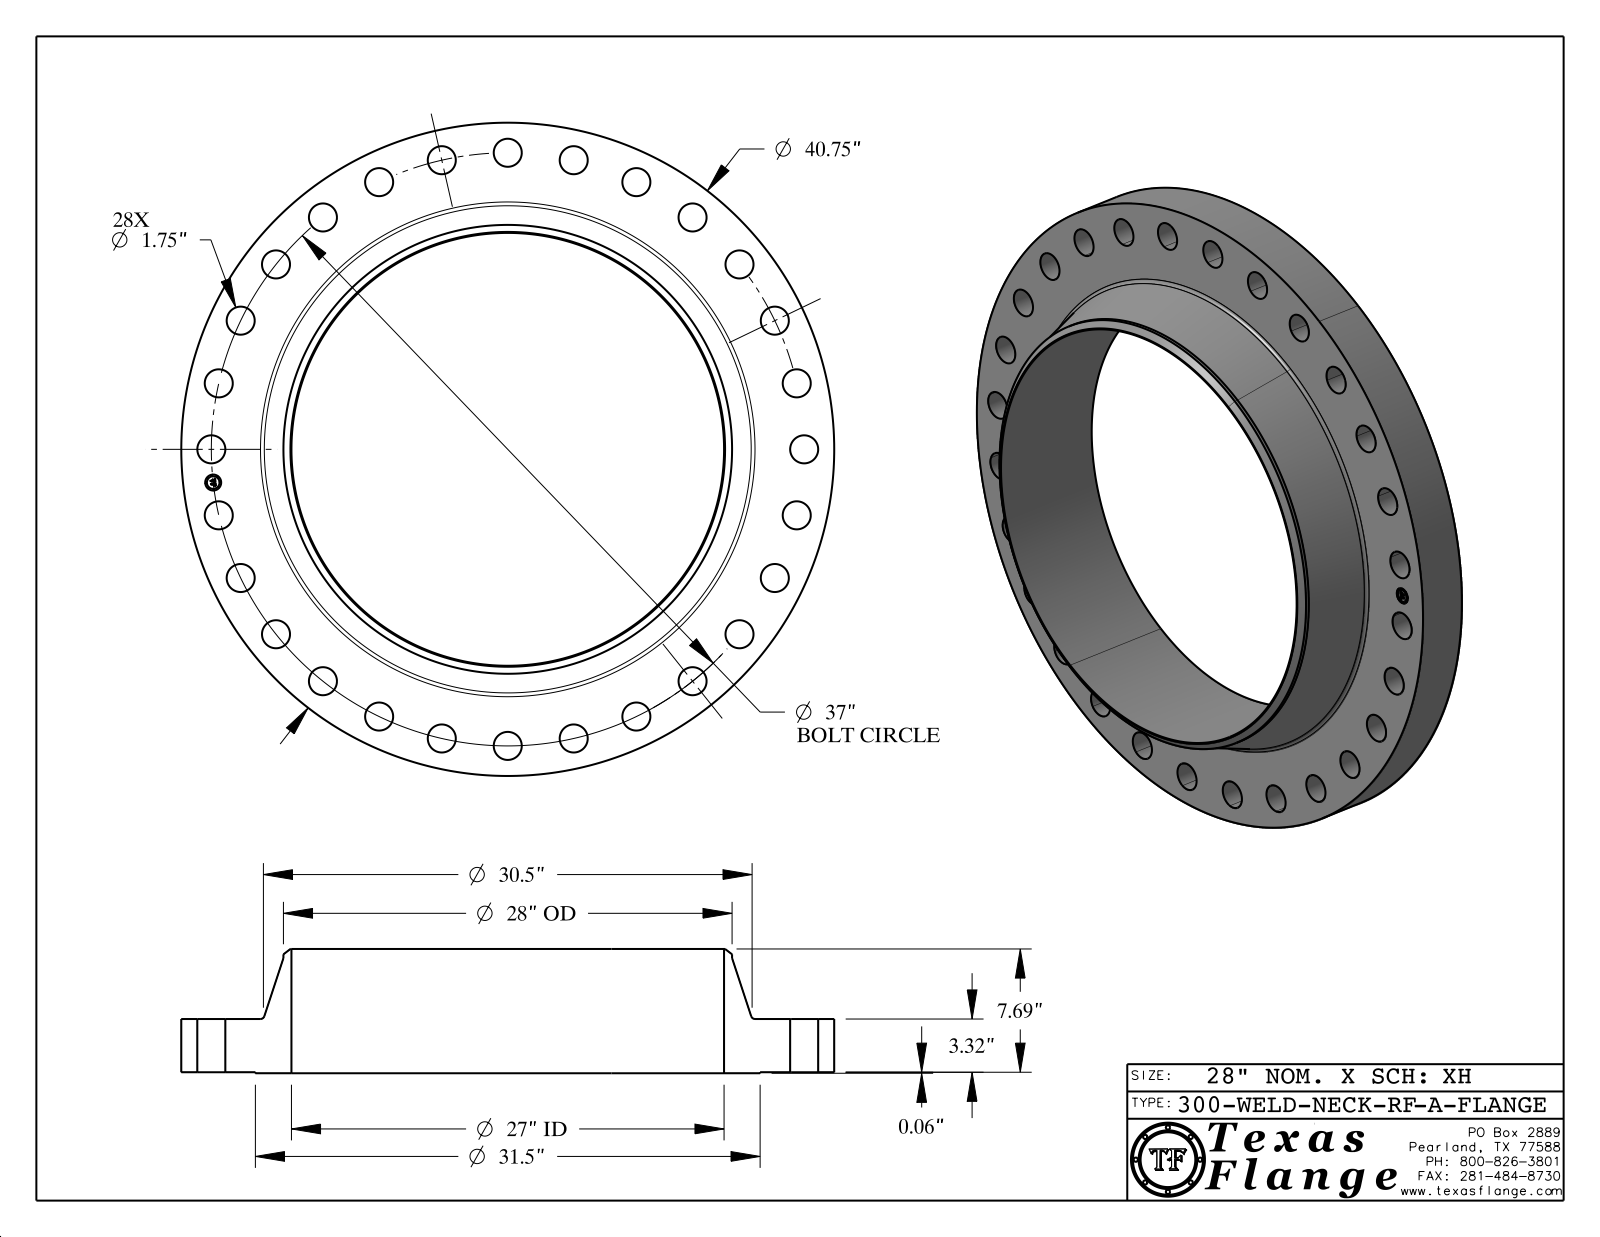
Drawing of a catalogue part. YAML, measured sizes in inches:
part_name: "300-WELD-NECK-RF, Series A"
step_written_by: "CATIA V5 STEP AP214 (AUTOMOTIVE_DESIGN)"
units: inches
bodies: {solids: 1, faces: 459, planar: 369, cylindrical: 84, other: 6}
overall_size: [40.75, 40.75, 7.753]
volume: 2616
surface_area: 3207
round_holes:
  - {diameter: 1.75, count: 28}
  - {diameter: 1, count: 1}
  - {diameter: 27, count: 1}
round_bosses_or_shafts:
  - {diameter: 0.061, count: 8}
  - {diameter: 40.75, count: 1}
  - {diameter: 31.5, count: 1}
  - {diameter: 28, count: 1}
  - {diameter: 0.788, count: 1}
face_to_face_distances: [3.32, 0.063, 3.383, 7.753, 7.69, 4.37, 0.015, 3.368, 3.305, 4.385]
hole_center_spacings: [18.5, 26.163, 31.329, 36.072, 36.767, 33.336, 4.143, 16.054]
